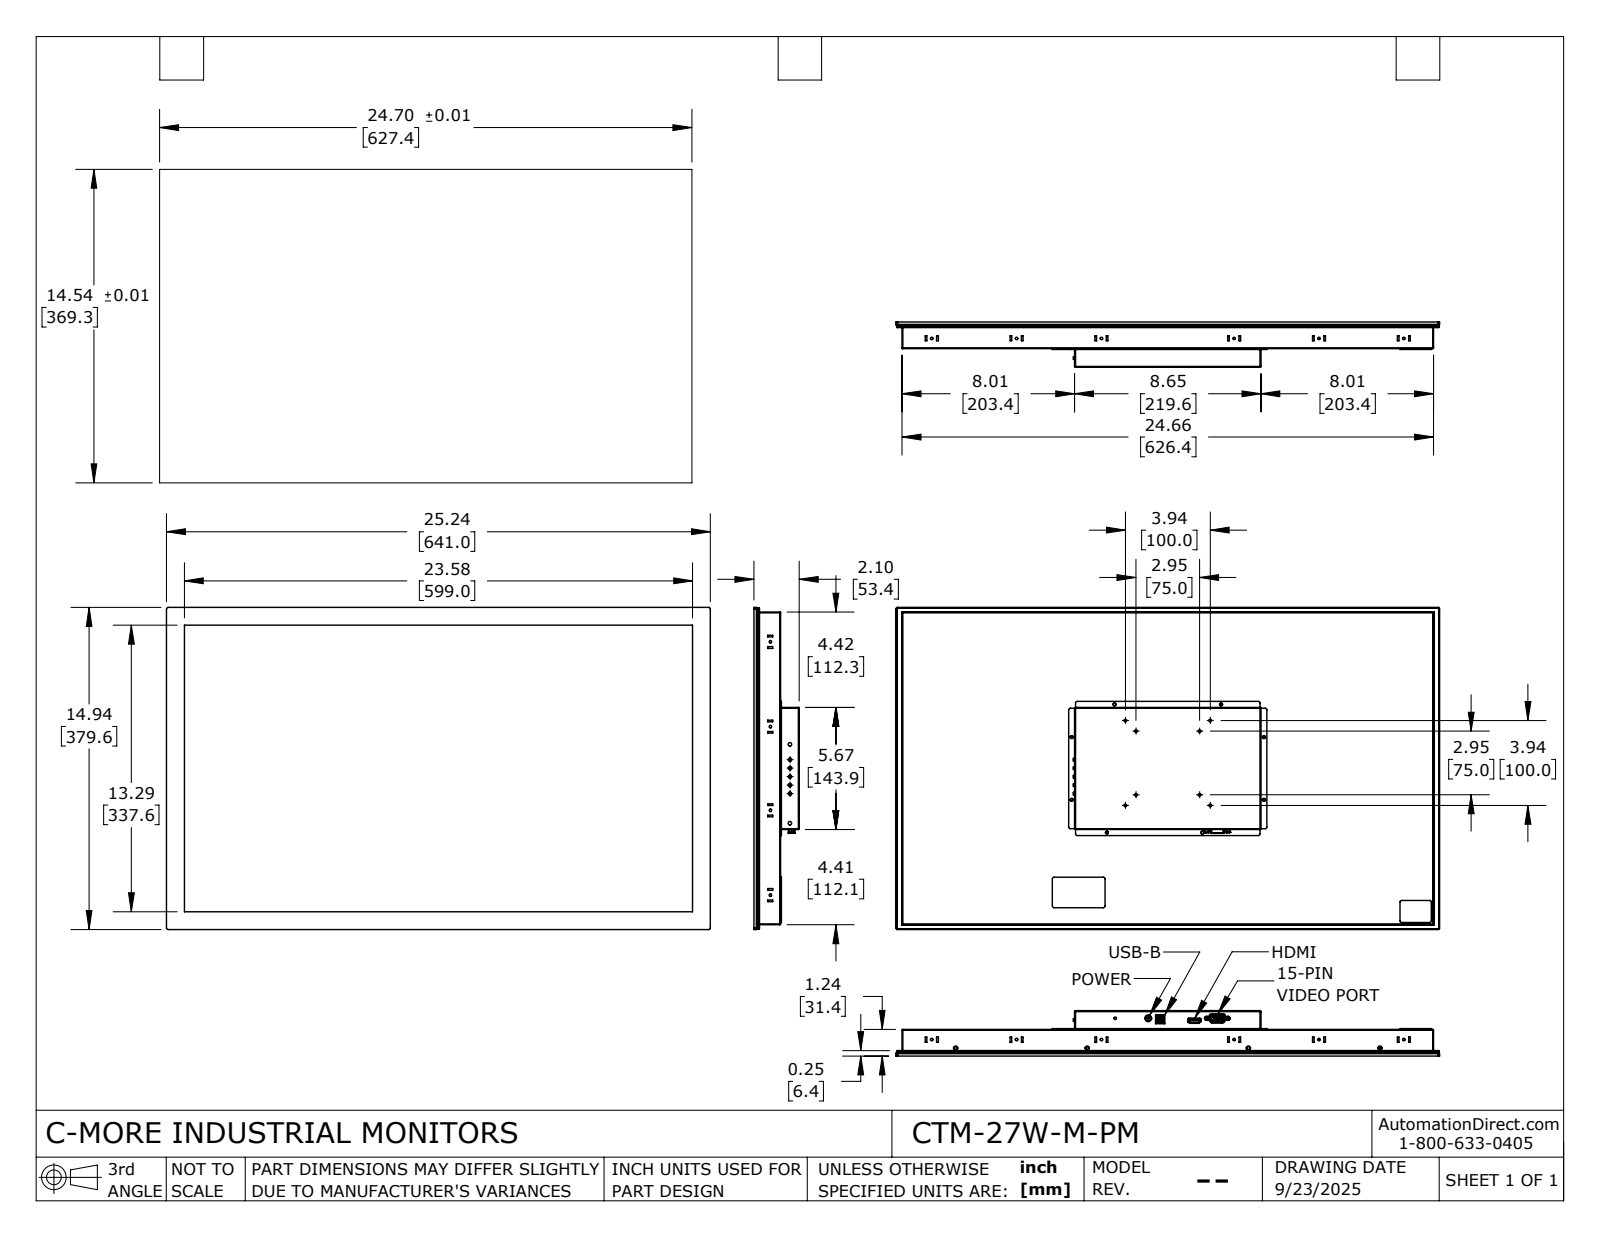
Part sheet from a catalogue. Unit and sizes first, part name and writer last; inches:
Units: inches
Overall size (bounding box): 25.236 × 14.943 × 2.104
Round holes (diameter × count): ⌀0.118 ×19, ⌀0.047 ×15, ⌀0.165 ×14, ⌀0.125 ×8, ⌀0.138 ×8, ⌀0.212 ×8, ⌀0.157 ×5, ⌀0.108 ×2, ⌀0.248 ×1, ⌀0.315 ×1
Round bosses / shafts (diameter × count): ⌀0.125 ×5, ⌀0.093 ×1
Partial cylindrical surfaces — rounded edges, fillets, slot ends (radius × count): R0.006 ×60, R0.079 ×55, R0.039 ×22, R0.02 ×11, R0.118 ×8, R0.197 ×7, R0.051 ×6, R0.063 ×6
Main face-to-face distances: 1.23, 1.238, 0.866, 2.096, 2.104, 0.039, 14.5, 1.102, 0.102, 1.063
Hole centre spacings: 0.09, 0.238, 0.156, 0.09, 3.937, 0.18, 0.18, 3.48
Volume: 486.3 in³ · Surface area: 973.5 in²
Bodies: 1 solid, 1303 faces (766 planar, 453 cylindrical, 84 other)
Part name (STEP PRODUCT): CTM-27W-M-PM-20250528
STEP written by: SolidWorks 2024 (AUTOMOTIVE_DESIGN)
